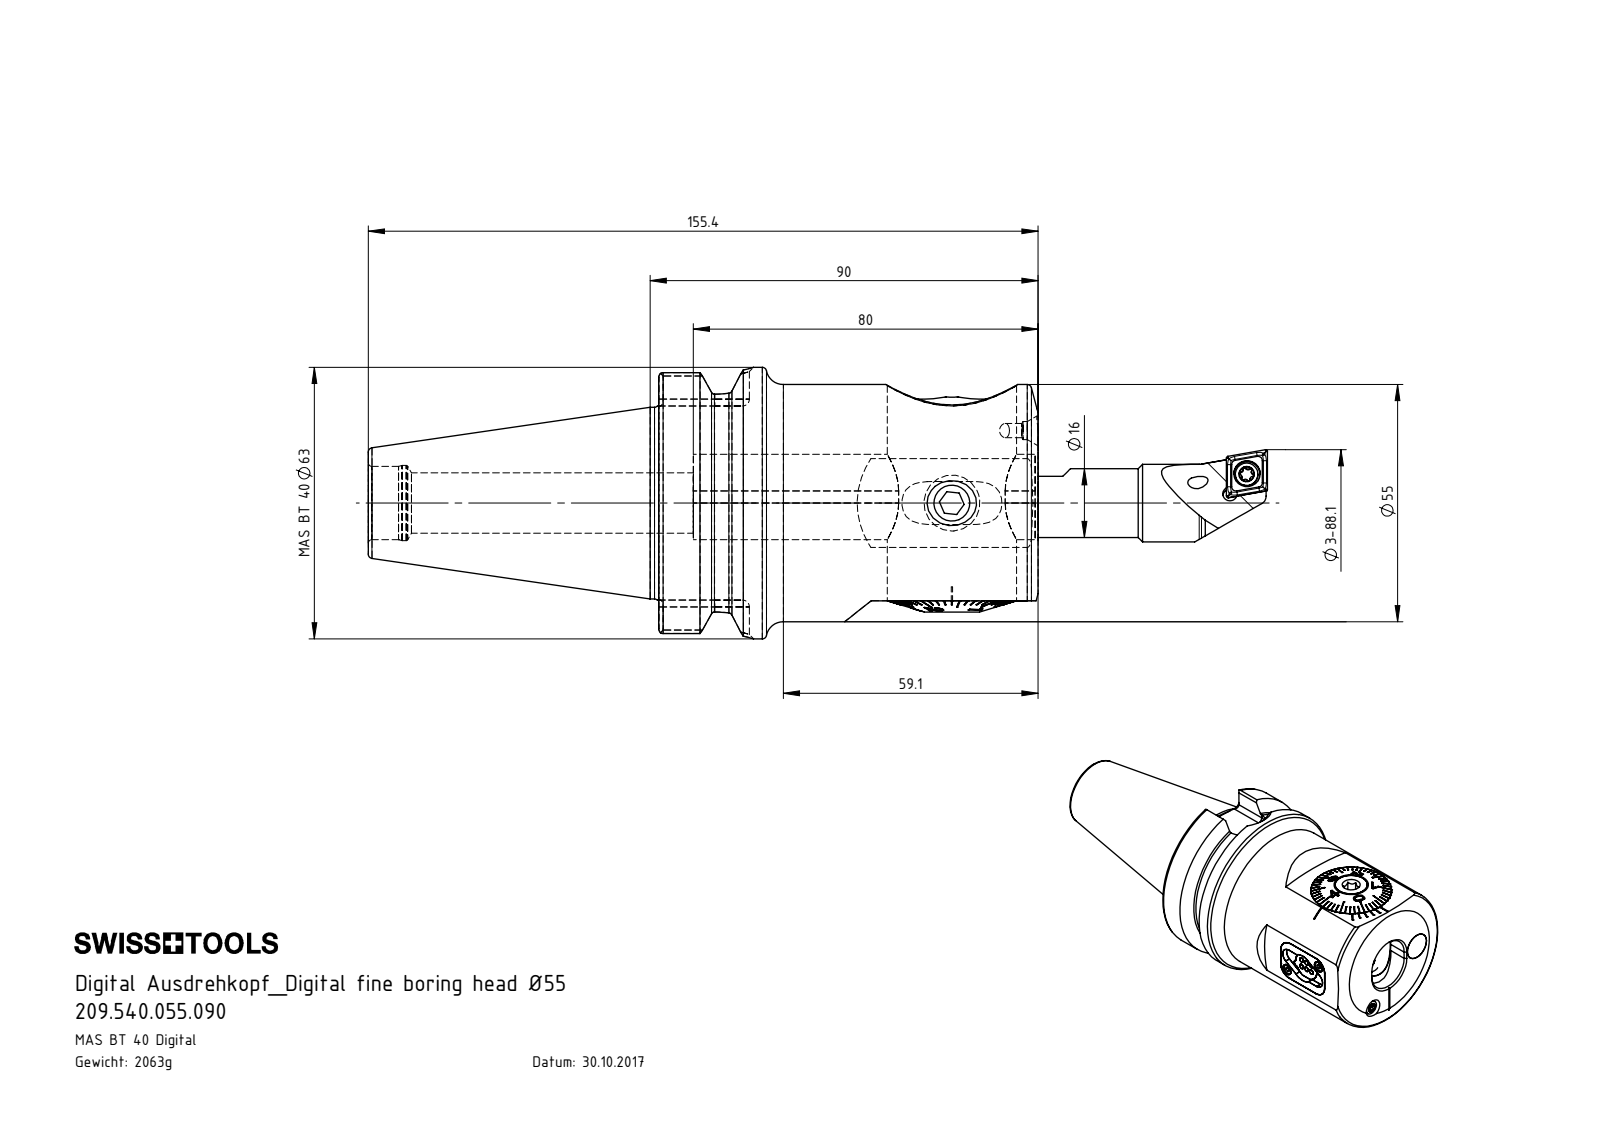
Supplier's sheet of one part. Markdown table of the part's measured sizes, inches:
| quantity | value |
| --- | --- |
| part name | A55-BG2.012.006_B; ISO 4762 - M2 x 6; A55-BG1.DA3.041_Dichtung; Fxx-BG7.DA1.0xx_A_F55 (+8 more) |
| STEP written by | SolidWorks 2017 (CONFIG_CONTROL_DESIGN) |
| units | inches |
| bodies | 27 solids, 1179 faces (485 planar, 309 cylindrical, 385 other) |
| overall size | 8.215 × 2.48 × 2.48 |
| volume | 16.1 in³ |
| surface area | 104.4 in² |
| round holes (diameter × count) | 0.126 × 4, 0.063 × 3, 0.13 × 3, 0.165 × 3, 0.335 × 3, 0.087 × 2, 0.118 × 2, 0.551 × 2, 0.173 × 1, 0.24 × 1, 0.315 × 1, 0.394 × 1 |
| round bosses / shafts (diameter × count) | 0.075 × 6, 0.394 × 3, 0.709 × 2, 0.207 × 2, 0.157 × 2, 0.15 × 2, 0.079 × 2, 2.48 × 1 |
| partial cylindrical surfaces (radius × count) | 0.013 × 12, 0.023 × 12, 0.047 × 8, 0.063 × 8, 0.043 × 6, 0.177 × 4, 0.126 × 3, 0.173 × 3 |
| main face-to-face distances | 3.465, 0.146, 0.079, 0.157, 1.136, 0.018, 0.11, 0.209, 0.047, 0.222 |
| hole center spacings | 0.161, 0.17, 0.285, 0.333, 0.375, 0.472, 0.499, 0.571 |
